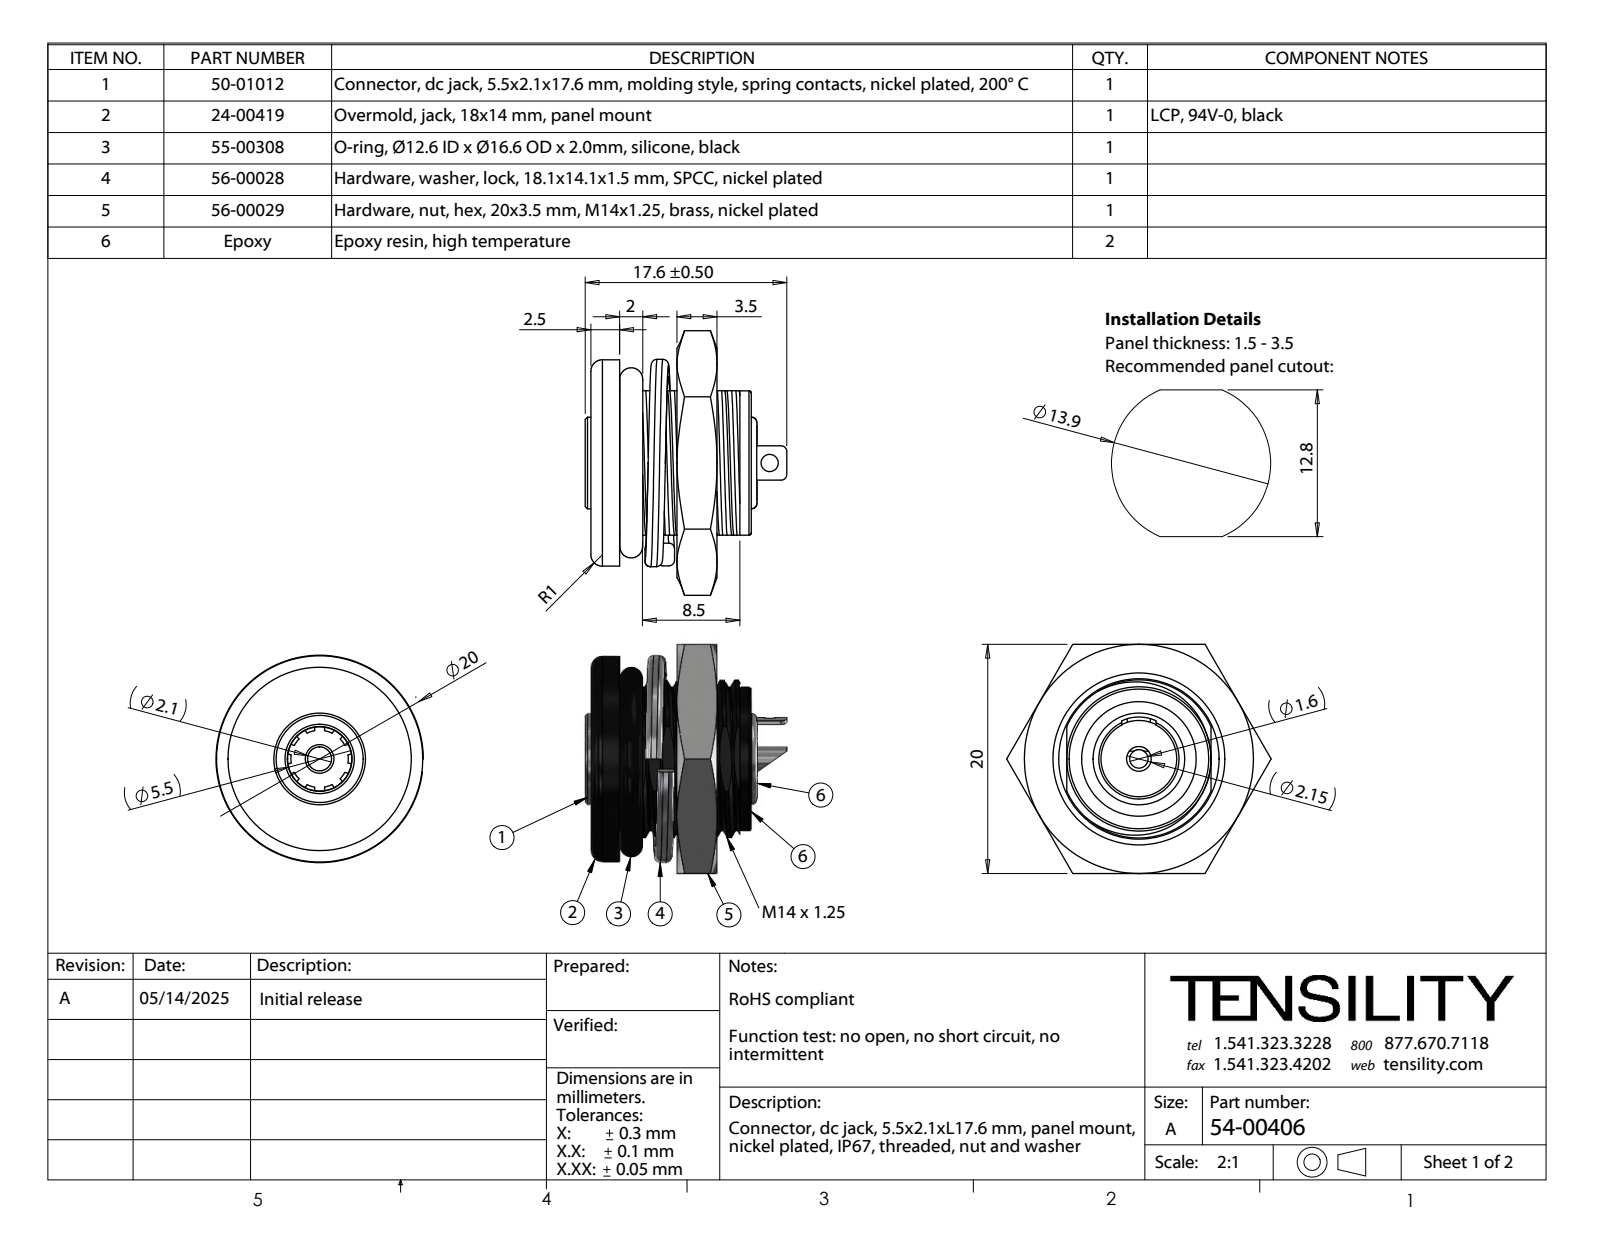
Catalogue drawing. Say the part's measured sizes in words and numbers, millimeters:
The part is named "50-01012; 50-01012 insulator_Insulator; 24-00419; 56-00029 (+6 more)". Its 3-D file was written by "SolidWorks 2021 (AUTOMOTIVE_DESIGN)". It is 8 solids with 289 faces: 101 planar, 81 cylindrical and 107 other. Overall it measures 23.09 by 20 by 17.6 millimeters. Its volume is 2 808 cubic millimeters and its surface area 4 239 square millimeters. Round holes: 2 of diameter 1.5, 1 of diameter 1.6, 1 of diameter 2.15, 1 of diameter 2.5, 1 of diameter 5.6, 1 of diameter 5.65, 1 of diameter 6.4, 1 of diameter 6.6, 1 of diameter 7.6, 1 of diameter 8, 1 of diameter 10, 1 of diameter 14. Round bosses or shafts: 1 of diameter 18, 1 of diameter 12.6, 1 of diameter 12.59, 1 of diameter 7.3, 1 of diameter 6.2, 1 of diameter 2.1. Partial cylindrical surfaces (rounded edges, fillets, slot ends): 2 of radius 0.5, 1 of radius 3.35, 1 of radius 6.9. The main face-to-face distances are 3.5, 7.51, 11.01, 2.5, 5.01, 8.51, 20, 8.5, 2, 1.
